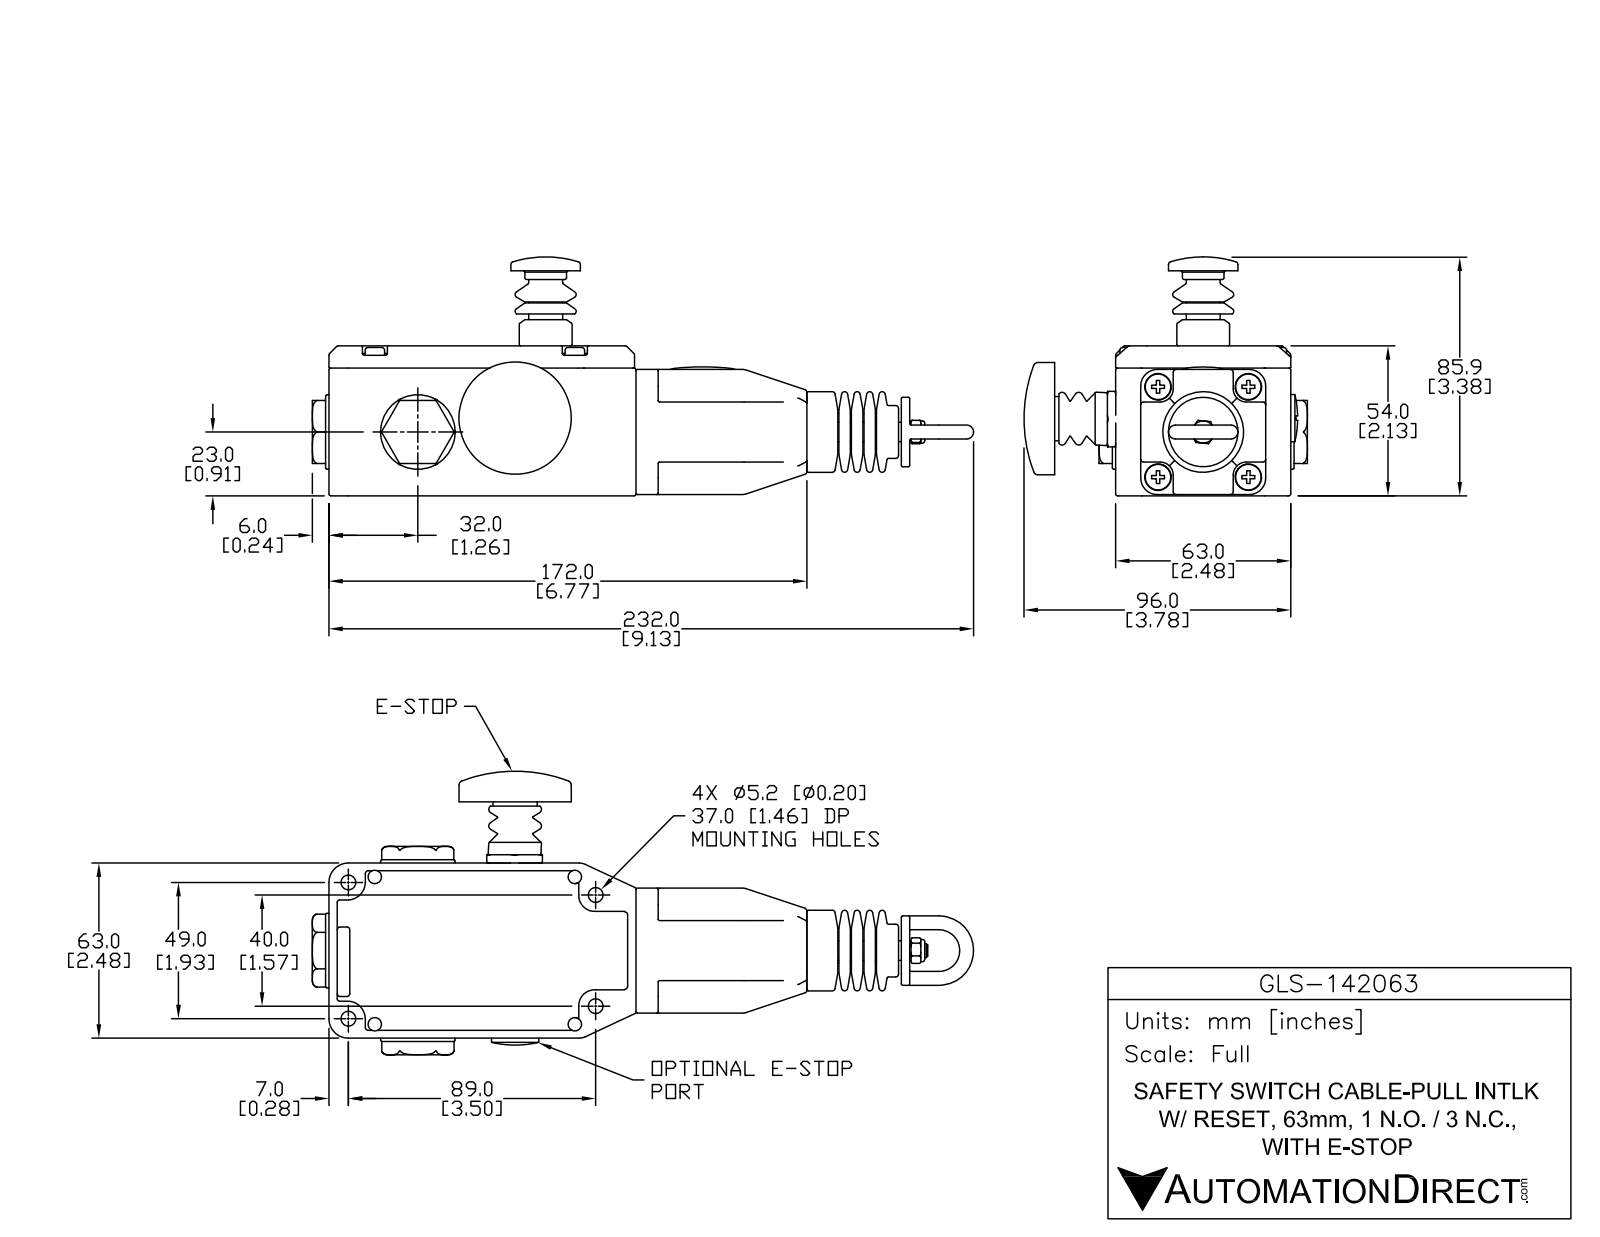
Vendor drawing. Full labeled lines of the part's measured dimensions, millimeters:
Part name (STEP PRODUCT): GLS-142063
STEP written by: SolidWorks 2013 (AUTOMOTIVE_DESIGN)
Units: millimetres
Bodies: 1 solid, 617 faces (210 planar, 201 cylindrical, 206 other)
Overall size (bounding box): 238 × 102.3 × 86
Volume: 492 222 mm³ · Surface area: 64 589 mm²
Round holes (diameter × count): ⌀4.75 ×4, ⌀9.5 ×4, ⌀5 ×2, ⌀5.2 ×2, ⌀34 ×1
Round bosses / shafts (diameter × count): ⌀9.2 ×4, ⌀6 ×4, ⌀26.8 ×2, ⌀25 ×2, ⌀19 ×2, ⌀12 ×2, ⌀5 ×2, ⌀40 ×1
Partial cylindrical surfaces — rounded edges, fillets, slot ends (radius × count): R0.5 ×42, R0.75 ×20, R1.1 ×6, R4 ×4, R4.5 ×4, R4.8 ×4, R16 ×4, R5.8 ×2
Main face-to-face distances: 53.68, 63, 54, 9, 11.7, 33.3, 45, 4.5, 49.5, 0.32
Hole centre spacings: 9.6, 9.62, 32.4, 32.6, 45.96, 46.61, 51.39, 52
